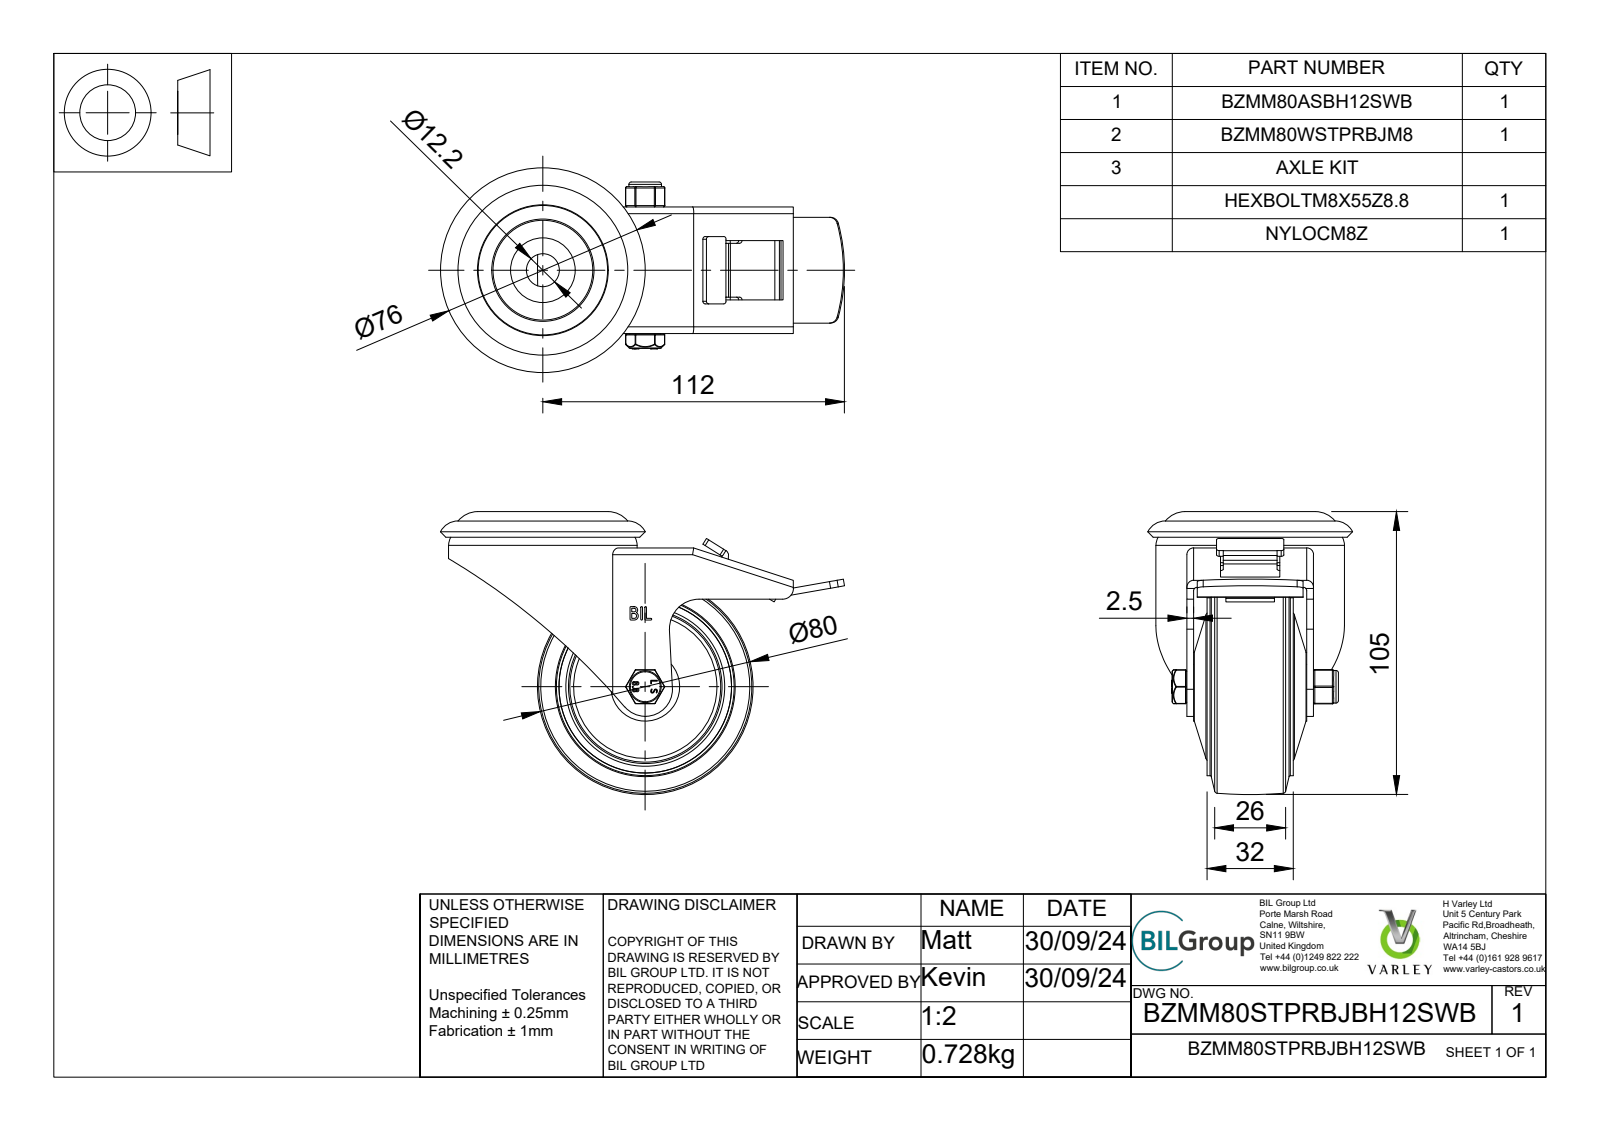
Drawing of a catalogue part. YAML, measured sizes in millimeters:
part_name: "BZMM80STPRBJBH12SWB v3; BZMM80ASBH12SWB - 42 v1; ZINC PLATED, PRESSED STEEL HEAD (1); ZINC PLATED, PRESSED STEEL BRAKE PEDAL (1) (+8 more)"
step_written_by: "Autodesk Translation Framework v13.20.0.188 (AUTOMOTIVE_DESIGN)"
units: millimeters
bodies: {solids: 24, faces: 987, planar: 425, cylindrical: 274, other: 288}
overall_size: [150, 105, 76]
volume: 176360
surface_area: 127910
round_holes:
  - {diameter: 0.66, count: 2}
  - {diameter: 8, count: 1}
  - {diameter: 8.2, count: 1}
  - {diameter: 8.5, count: 1}
  - {diameter: 8.6, count: 1}
  - {diameter: 12.2, count: 1}
  - {diameter: 20, count: 1}
  - {diameter: 22.5, count: 1}
  - {diameter: 30, count: 1}
  - {diameter: 31, count: 1}
  - {diameter: 32, count: 1}
  - {diameter: 32.5, count: 1}
round_bosses_or_shafts:
  - {diameter: 70, count: 1}
  - {diameter: 66, count: 1}
  - {diameter: 56, count: 1}
  - {diameter: 49.5, count: 1}
  - {diameter: 43, count: 1}
  - {diameter: 39, count: 1}
  - {diameter: 38, count: 1}
  - {diameter: 34.5, count: 1}
partial_cylinders:
  - {radius: 0.75, count: 48}
  - {radius: 0.5, count: 26}
  - {radius: 0.25, count: 12}
  - {radius: 1, count: 6}
  - {radius: 1.25, count: 6}
  - {radius: 2, count: 5}
  - {radius: 2.5, count: 5}
  - {radius: 0.33, count: 4}
face_to_face_distances: [2.5, 44.5, 21.5, 11, 4, 19, 4.5, 7.5, 18, 5]
hole_center_spacings: [3.22, 2.49]
